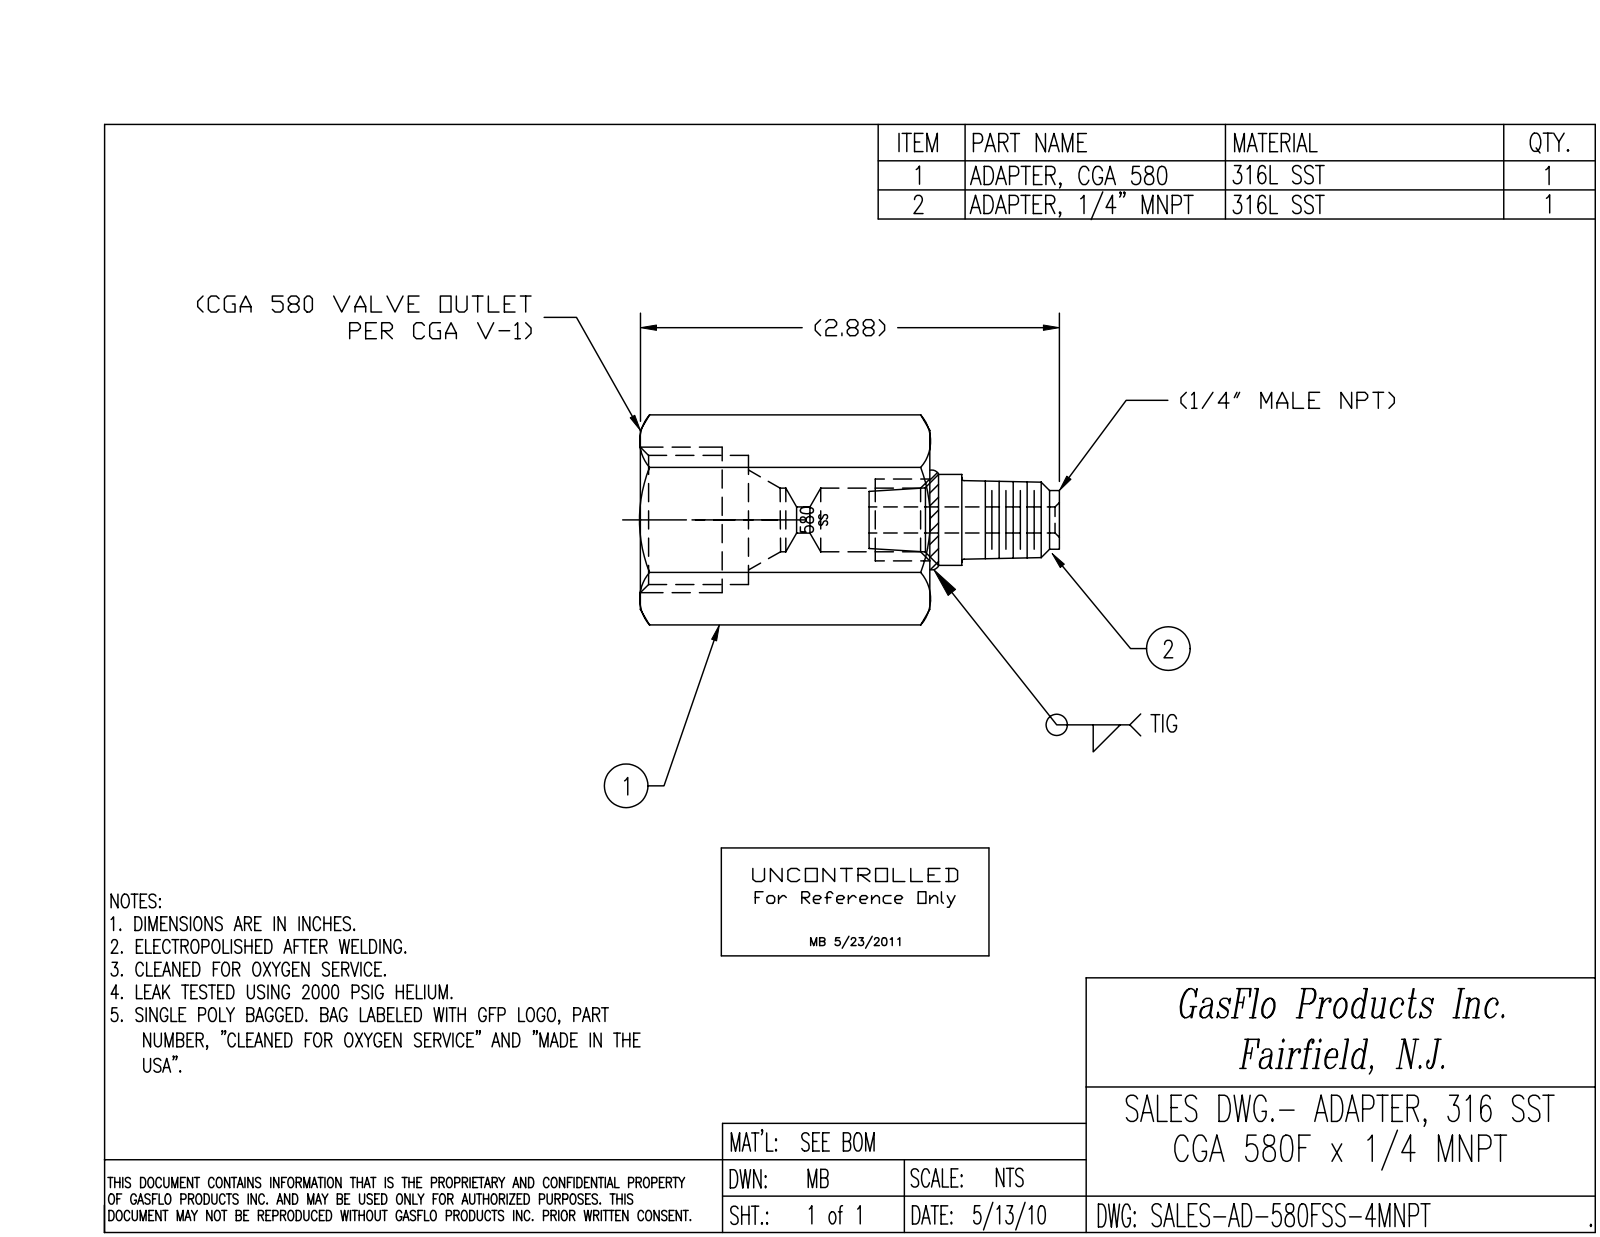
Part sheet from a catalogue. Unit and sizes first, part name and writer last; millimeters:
Units: millimetres
Overall size (bounding box): 73.2 × 36.7 × 31.8
Round holes (diameter × count): ⌀4.3 ×1, ⌀4.7 ×1, ⌀10.7 ×1, ⌀10.7 ×1, ⌀22.7 ×1
Round bosses / shafts (diameter × count): ⌀15.9 ×1, ⌀13.7 ×1, ⌀10.7 ×1
Main face-to-face distances: 31.8, 31.8, 50.8, 33.4, 17.4, 10.9, 22.5, 39.9, 22.4, 33.2
Volume: 37 030 mm³ · Surface area: 12 720 mm²
Bodies: 2 solids, 117 faces (20 planar, 33 cylindrical, 64 other)
Part name (STEP PRODUCT): PRT-001130; AD-580FSS-4MNPT; PRT-000394_AD-XXXSS-4MNPT
STEP written by: SolidWorks 2018 (CONFIG_CONTROL_DESIGN)
